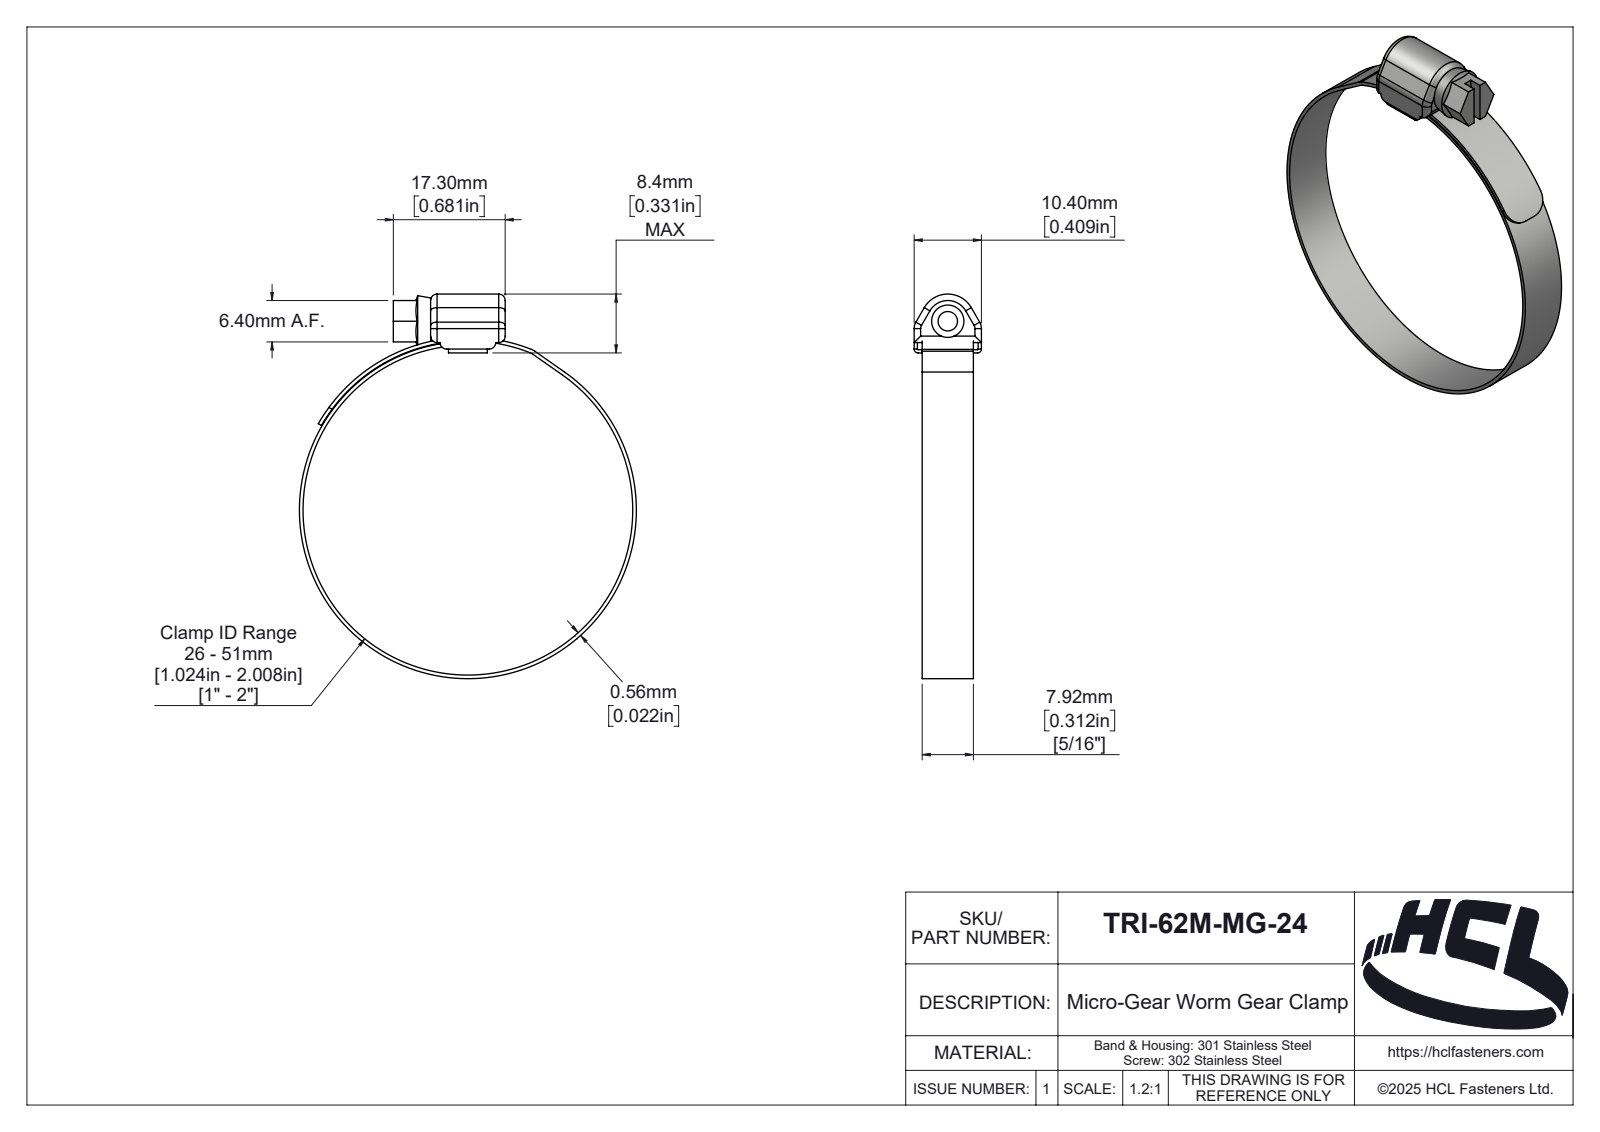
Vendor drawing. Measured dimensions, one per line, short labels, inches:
name: TRI-62M-MG-24
written by: SolidWorks 2025 (AUTOMOTIVE_DESIGN)
unit: in
bodies: 3 solids, 186 faces (38 planar, 87 cylindrical, 61 other)
size: 2.341 × 2.052 × 0.409
volume: 0.109 in³; area: 6.803 in²
holes: 1× ⌀0.197, 1× ⌀2.008
bosses: 1× ⌀2.052
rounds: 12× R0.039, 3× R0.079, 2× R0.004, 2× R0.024, 2× R0.118, 1× R0.01, 1× R0.04, 1× R0.05
face distances: 0.312, 0.043, 0.02, 0.049, 0.361, 0.063, 0.022, 0.244, 0.409, 0.227
